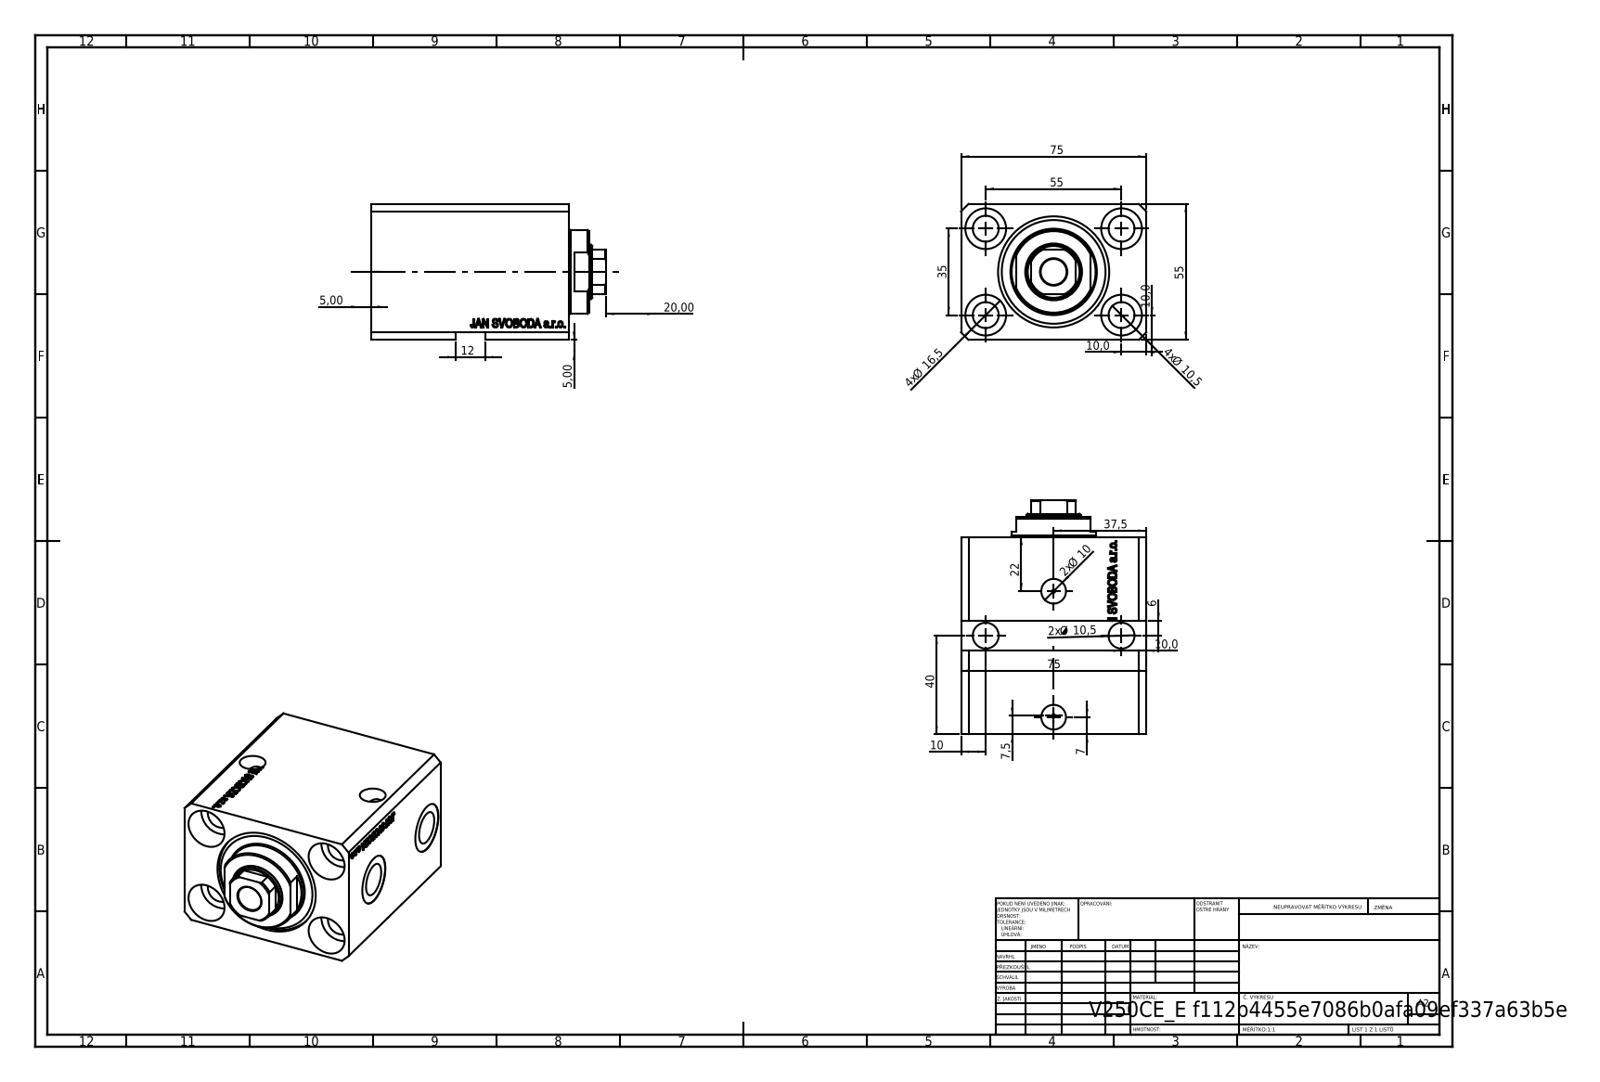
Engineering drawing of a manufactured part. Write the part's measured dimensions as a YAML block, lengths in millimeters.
part_name: "V250CE_C_VCP; V250CE_E_Body; V250CE_VC_E"
step_written_by: "SolidWorks 2019 (CONFIG_CONTROL_DESIGN)"
units: millimeters
bodies: {solids: 3, faces: 894, planar: 438, cylindrical: 84, other: 372}
overall_size: [94.9, 75, 55]
volume: 275433
surface_area: 69837
round_holes:
  - {diameter: 10.5, count: 7}
  - {diameter: 1.25, count: 4}
  - {diameter: 16.5, count: 4}
  - {diameter: 10, count: 2}
  - {diameter: 13.16, count: 2}
  - {diameter: 20, count: 2}
  - {diameter: 22, count: 1}
  - {diameter: 32, count: 1}
  - {diameter: 45, count: 1}
round_bosses_or_shafts:
  - {diameter: 34, count: 1}
partial_cylinders:
  - {radius: 10.5, count: 1}
face_to_face_distances: [55, 75, 80, 52.9, 27.1, 43, 9.9, 70.1, 11, 69]
hole_center_spacings: [32.6, 55, 32.87, 35, 42.55, 42.96, 65.19, 0.53]
